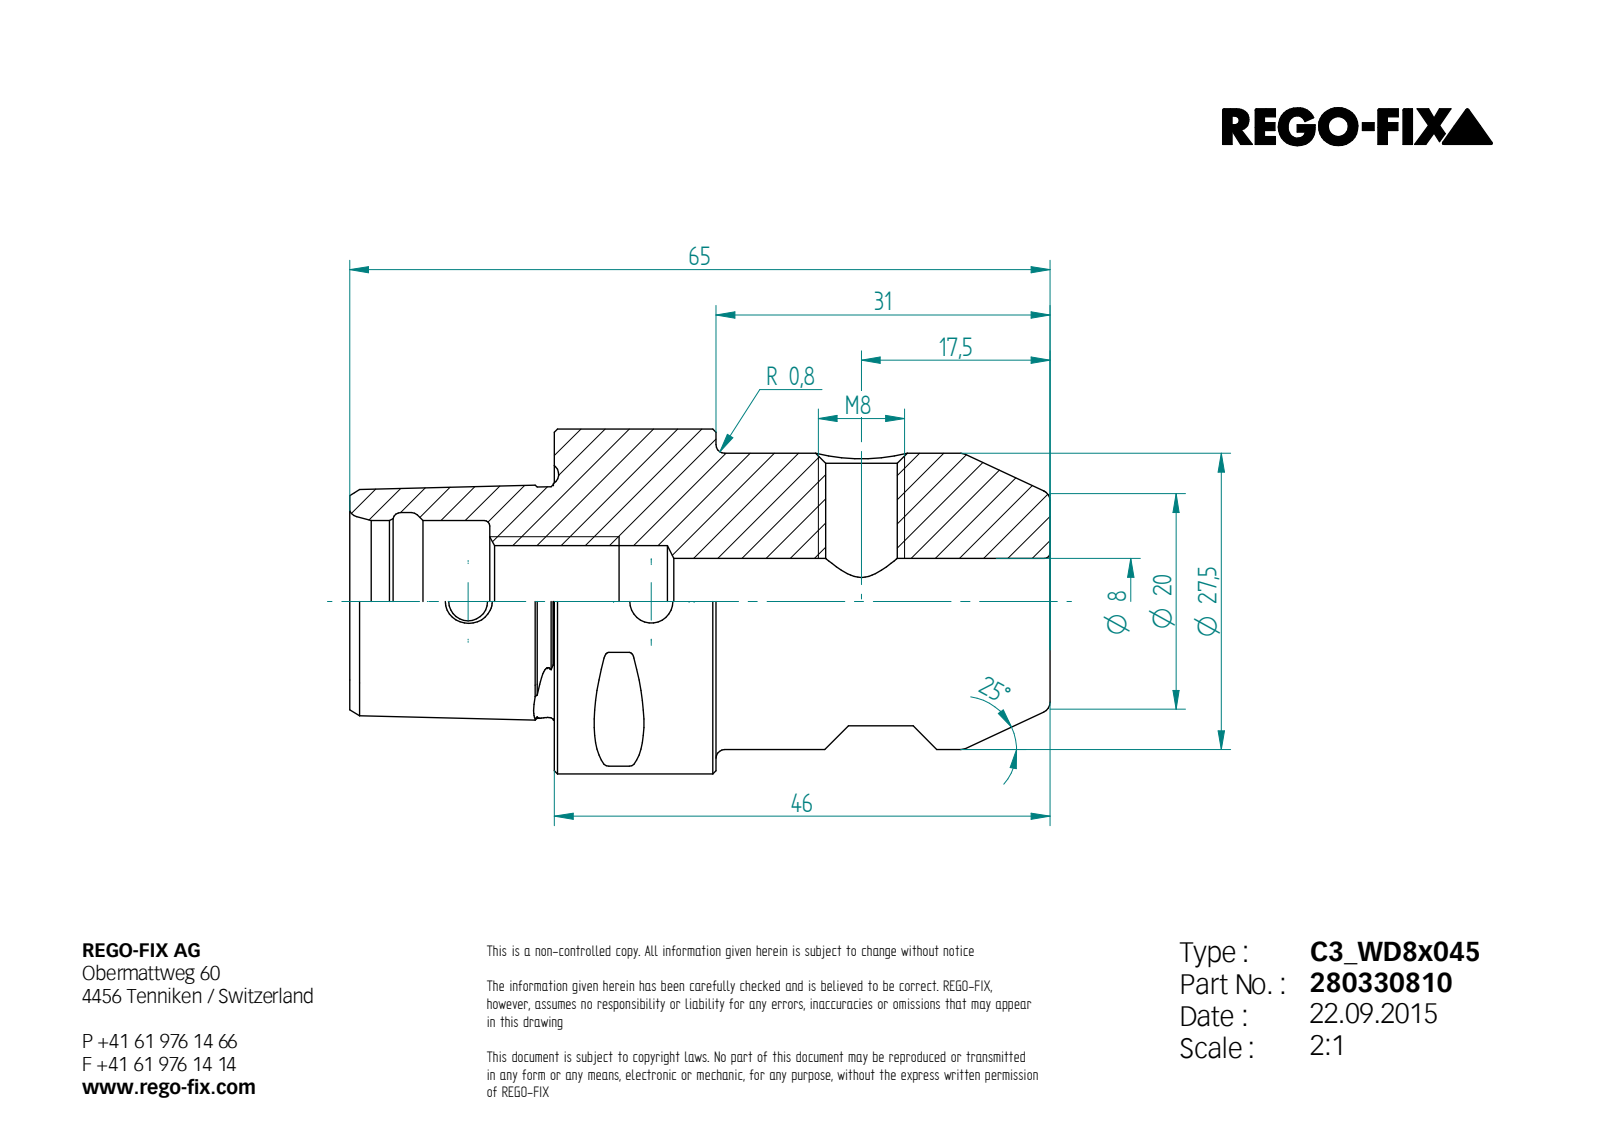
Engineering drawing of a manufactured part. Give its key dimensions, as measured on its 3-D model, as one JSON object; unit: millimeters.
{"step_written_by": "Unknown (AUTOMOTIVE_DESIGN)", "units": "millimeters", "bodies": {"solids": 1, "faces": 103, "planar": 23, "cylindrical": 19, "other": 61}, "overall_size": [65, 32, 32], "volume_mm3": 29626, "surface_area_mm2": 8845, "round_holes": [[3.6, 1], [4, 1], [6.65, 1], [8, 1], [10.38, 1], [15, 1], [16.5, 1]], "round_bosses_or_shafts": [[32, 1], [27.5, 1]], "partial_cylinders_radius": [[0.5, 8]], "face_to_face_distances": [46, 15, 31, 19, 34, 65, 12.02, 28.3, 13, 6], "hole_center_spacings": [17]}
